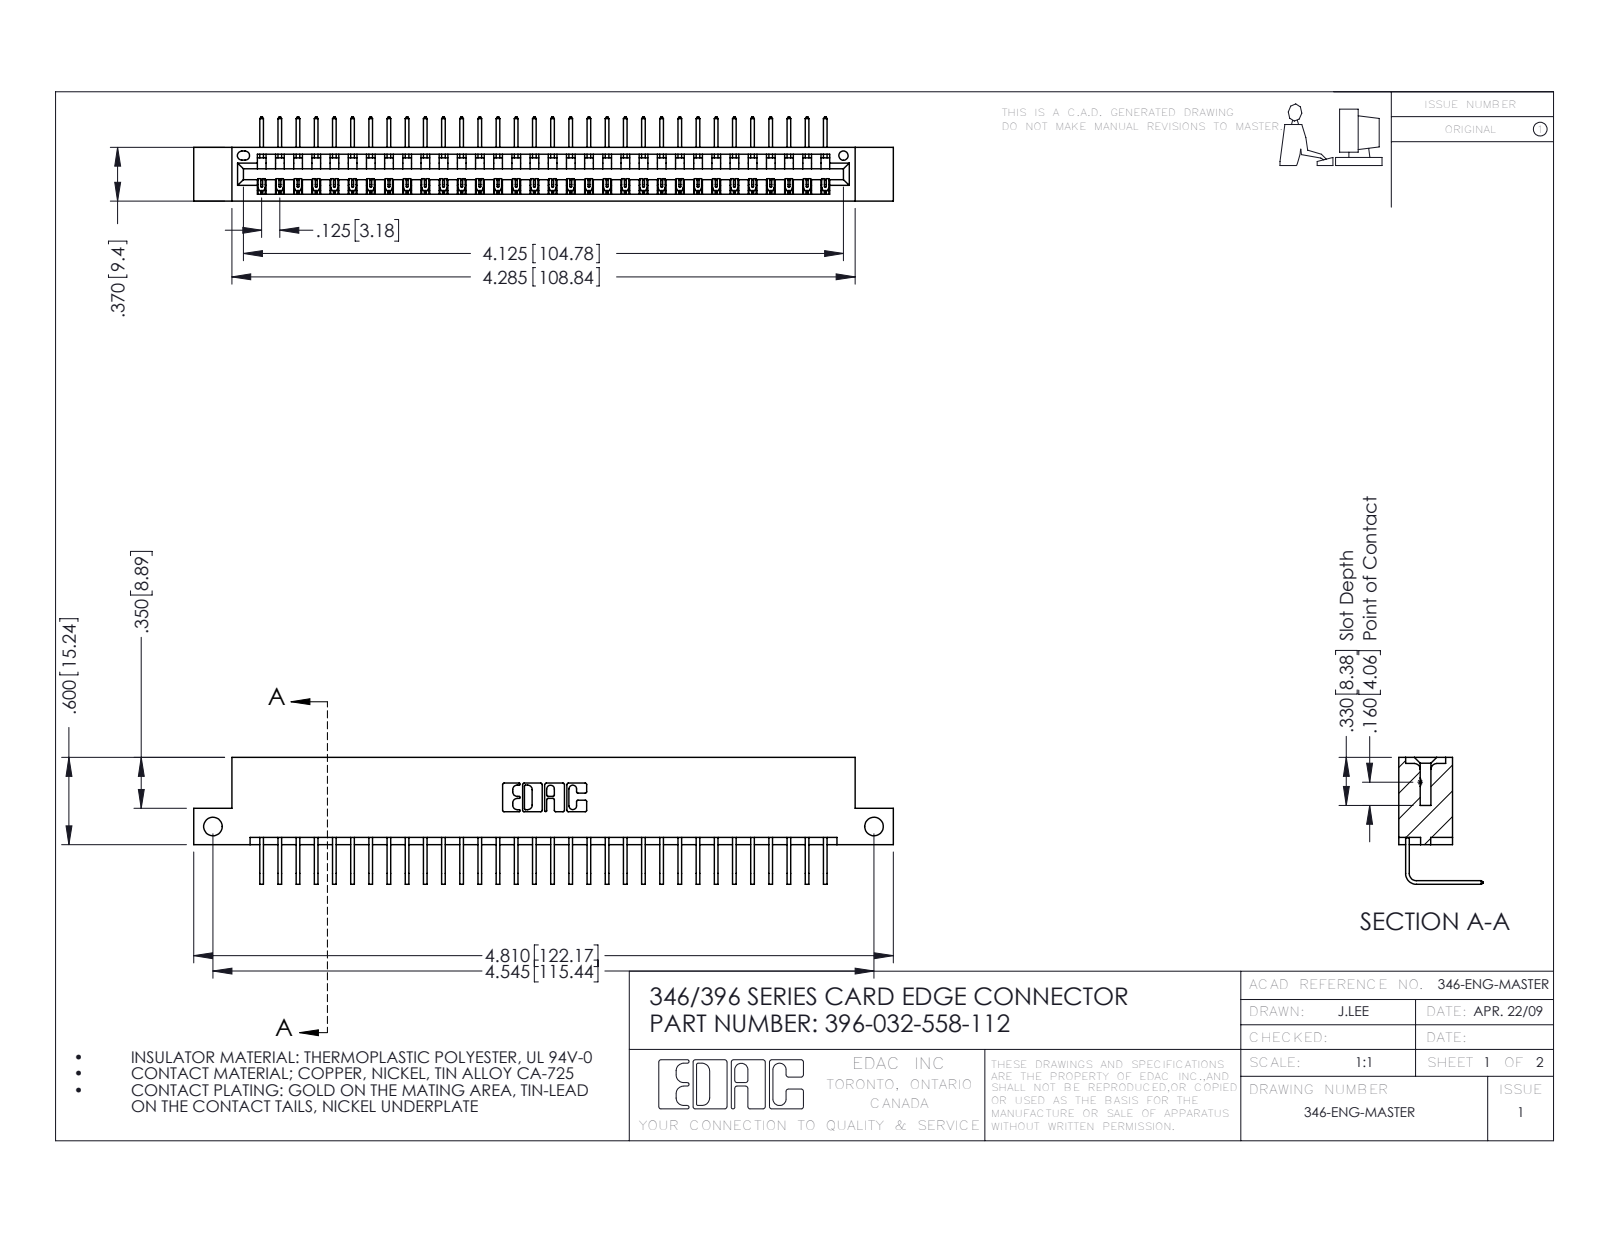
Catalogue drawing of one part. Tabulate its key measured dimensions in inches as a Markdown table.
| quantity | value |
| --- | --- |
| part name | 345-292-001_558 Tail - 2; 346 Part_Flush Mounting Lugs - Side Mount; 396-032-558-112 |
| STEP written by | SolidWorks 2016 (CONFIG_CONTROL_DESIGN) |
| units | inches |
| bodies | 33 solids, 2042 faces (1420 planar, 622 cylindrical, 0 other) |
| overall size | 4.81 × 0.873 × 0.58 |
| volume | 0.711 in³ |
| surface area | 23.15 in² |
| round holes (diameter × count) | 0.128 × 2, 0.064 × 1 |
| partial cylindrical surfaces (radius × count) | 0.006 × 64, 0.01 × 22, 0.007 × 6, 0.031 × 6, 0.026 × 3, 0.031 × 2, 0.04 × 2, 0.014 × 1 |
| main face-to-face distances | 0.322, 0.048, 0.37, 0.25, 0.298, 0.025, 0.072, 0.148, 0.222, 0.1 |
| hole center spacings | 4.545 |
